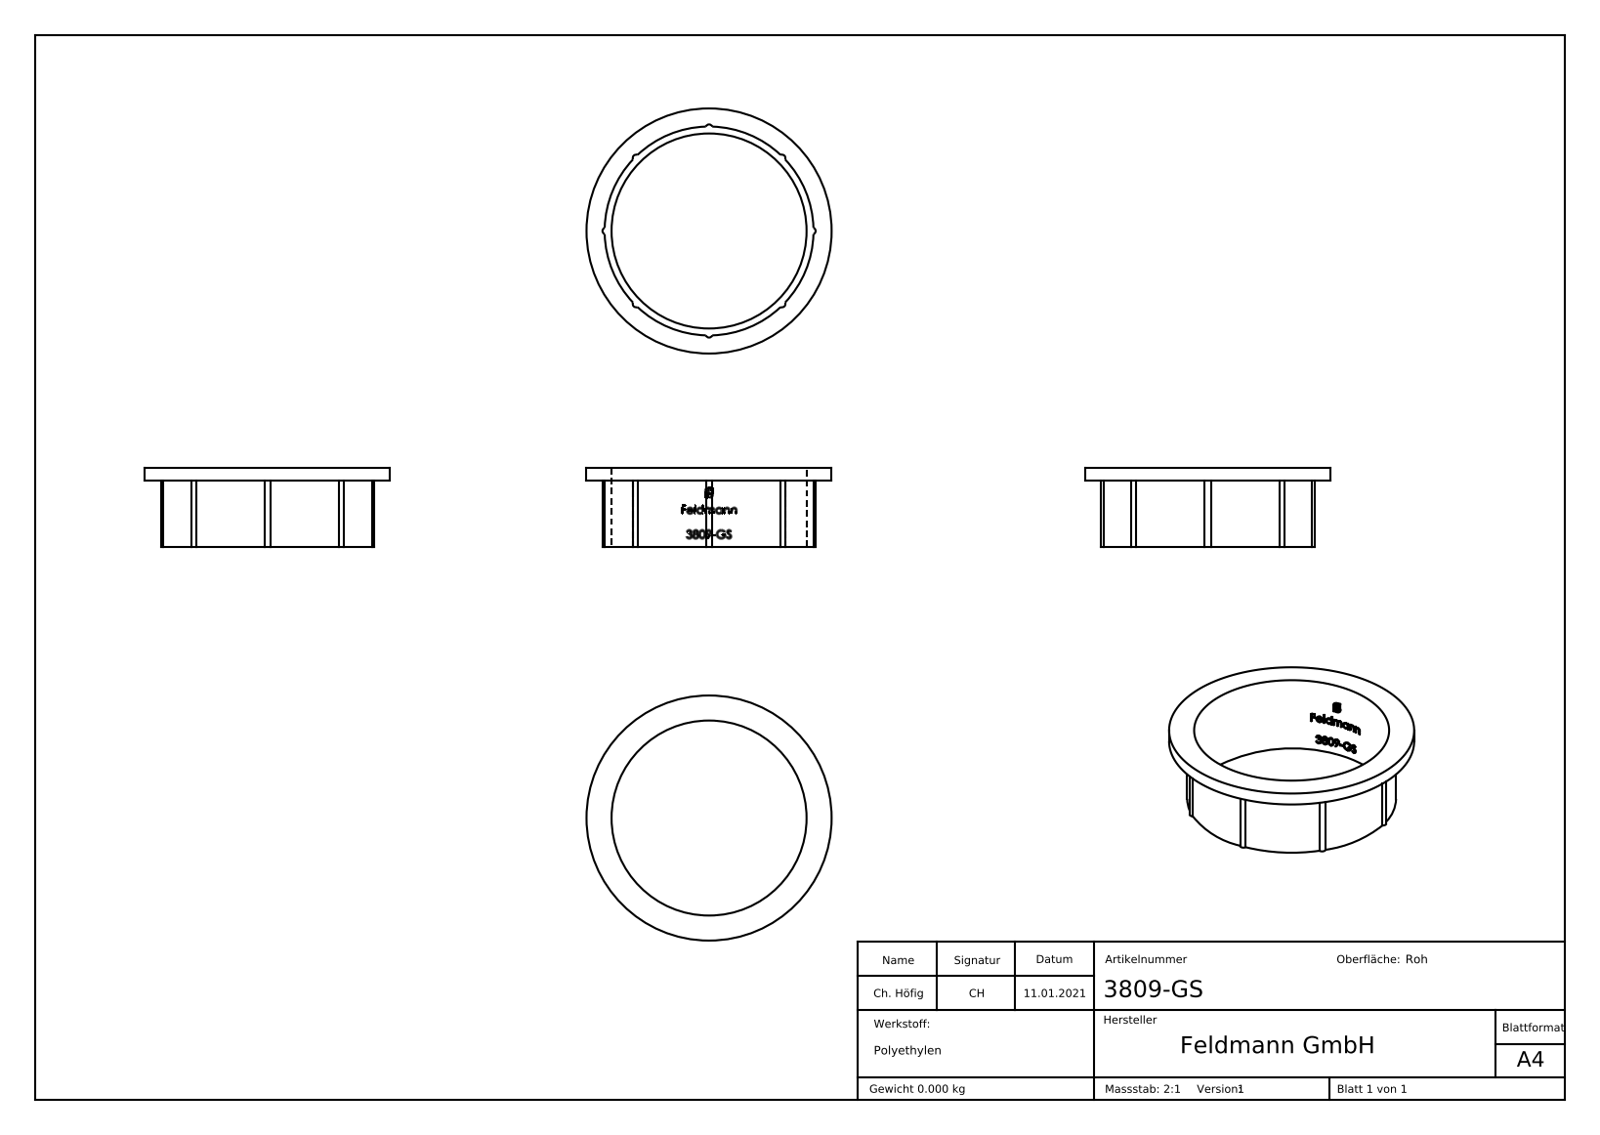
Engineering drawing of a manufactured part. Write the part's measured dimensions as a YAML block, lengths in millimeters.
part_name: "3809-GS"
step_written_by: "SolidWorks 2018 (CONFIG_CONTROL_DESIGN)"
units: millimeters
bodies: {solids: 1, faces: 292, planar: 93, cylindrical: 58, other: 141}
overall_size: [23, 23, 7.5]
volume: 431
surface_area: 1226
round_holes:
  - {diameter: 18.3, count: 1}
round_bosses_or_shafts:
  - {diameter: 23, count: 1}
  - {diameter: 19.6, count: 1}
partial_cylinders:
  - {radius: 0.33, count: 8}
  - {radius: 9.25, count: 1}
face_to_face_distances: [1.2, 6.3, 7.5, 1.78, 0.67, 0.99, 1.21, 0.83, 3.15, 2.77]
